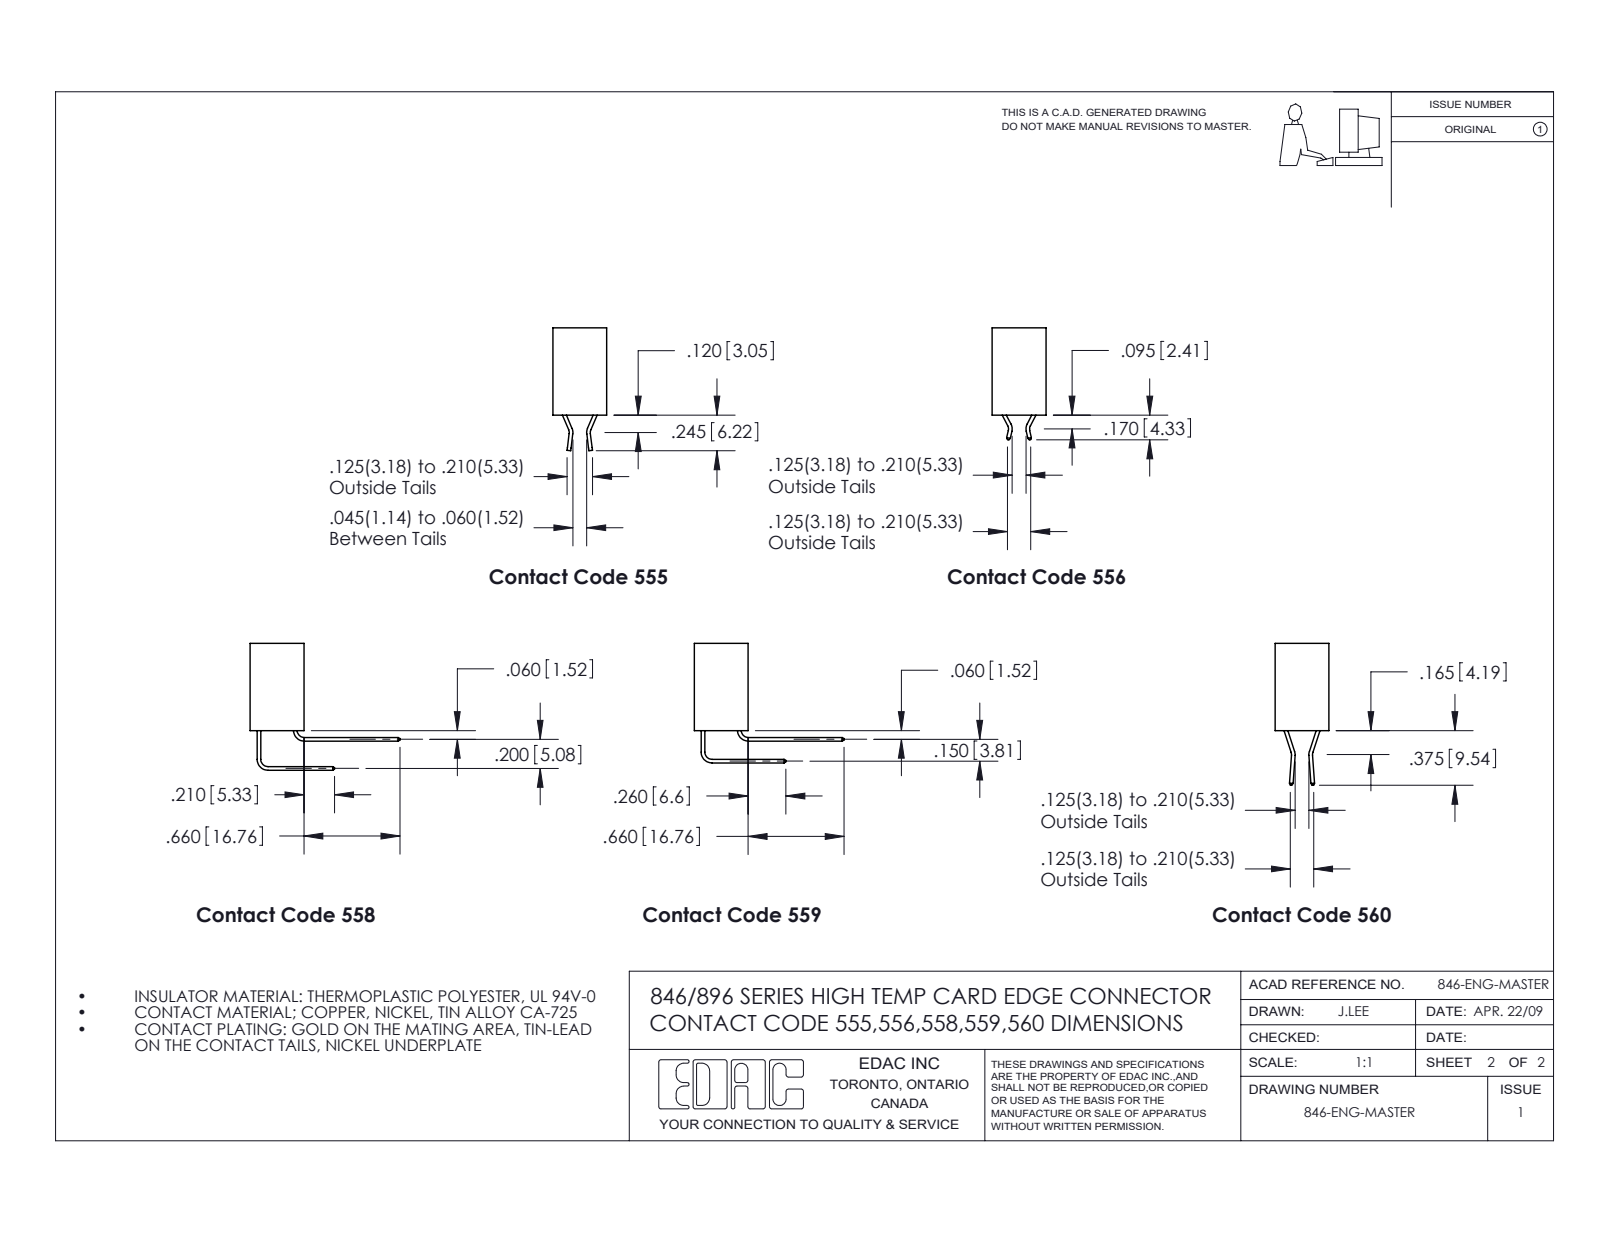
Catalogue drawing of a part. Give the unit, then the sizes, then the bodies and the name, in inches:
Units: inches
Overall size (bounding box): 2.66 × 1.03 × 0.823
Round holes (diameter × count): ⌀0.064 ×1
Partial cylindrical surfaces — rounded edges, fillets, slot ends (radius × count): R0.006 ×57, R0.01 ×22, R0.007 ×6, R0.031 ×6, R0.026 ×3, R0.014 ×2, R0.022 ×2, R0.024 ×2
Main face-to-face distances: 0.048, 0.322, 0.025, 0.25, 0.37, 0.072, 0.298, 0.275, 0.148, 0.222
Volume: 0.44 in³ · Surface area: 16.67 in²
Bodies: 39 solids, 2166 faces (1478 planar, 688 cylindrical, 0 other)
Part name (STEP PRODUCT): 345-292-001_559 Tail - 2; 346 Part_No Mounting Lugs; 345-292-001_558 559 Tail - 1; 346-038-559-201
STEP written by: SolidWorks 2016 (CONFIG_CONTROL_DESIGN)
